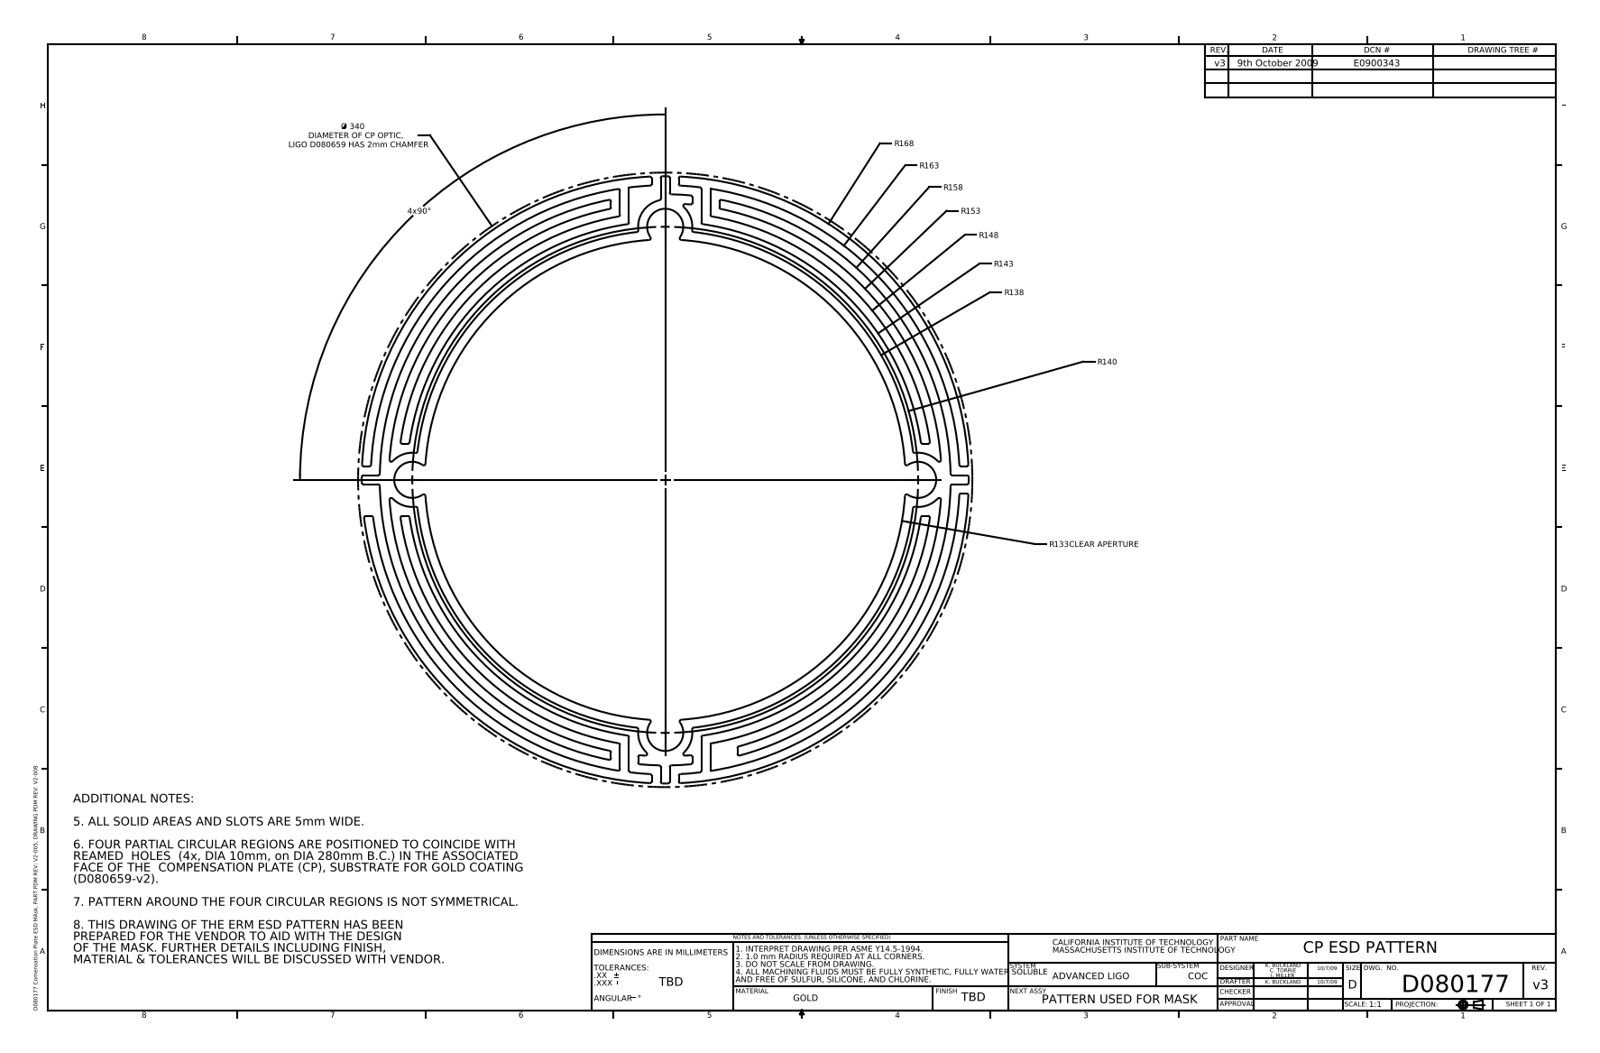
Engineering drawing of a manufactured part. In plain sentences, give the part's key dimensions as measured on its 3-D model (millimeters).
The part is named "D080177 Comensation Plate ESD Pattern-v3". Its 3-D file was written by "SolidWorks 2009 (AUTOMOTIVE_DESIGN)". It is 5 solids with 211 faces: 45 planar, 166 cylindrical and 0 other. Overall it measures 336 by 336 by 6.35 millimeters. Its volume is 116 184 cubic millimeters and its surface area 82 617 square millimeters. Round holes: 1 of diameter 266, 1 of diameter 286, 1 of diameter 306, 1 of diameter 326. Round bosses or shafts: 1 of diameter 336, 1 of diameter 316, 1 of diameter 296, 1 of diameter 276. Partial cylindrical surfaces (rounded edges, fillets, slot ends): 89 of radius 1, 4 of radius 10, 4 of radius 15. The main face-to-face distances are 6.35, 5, 22.5, 17.5, 27.5, 45, 40, 10, 50, 12.5.
